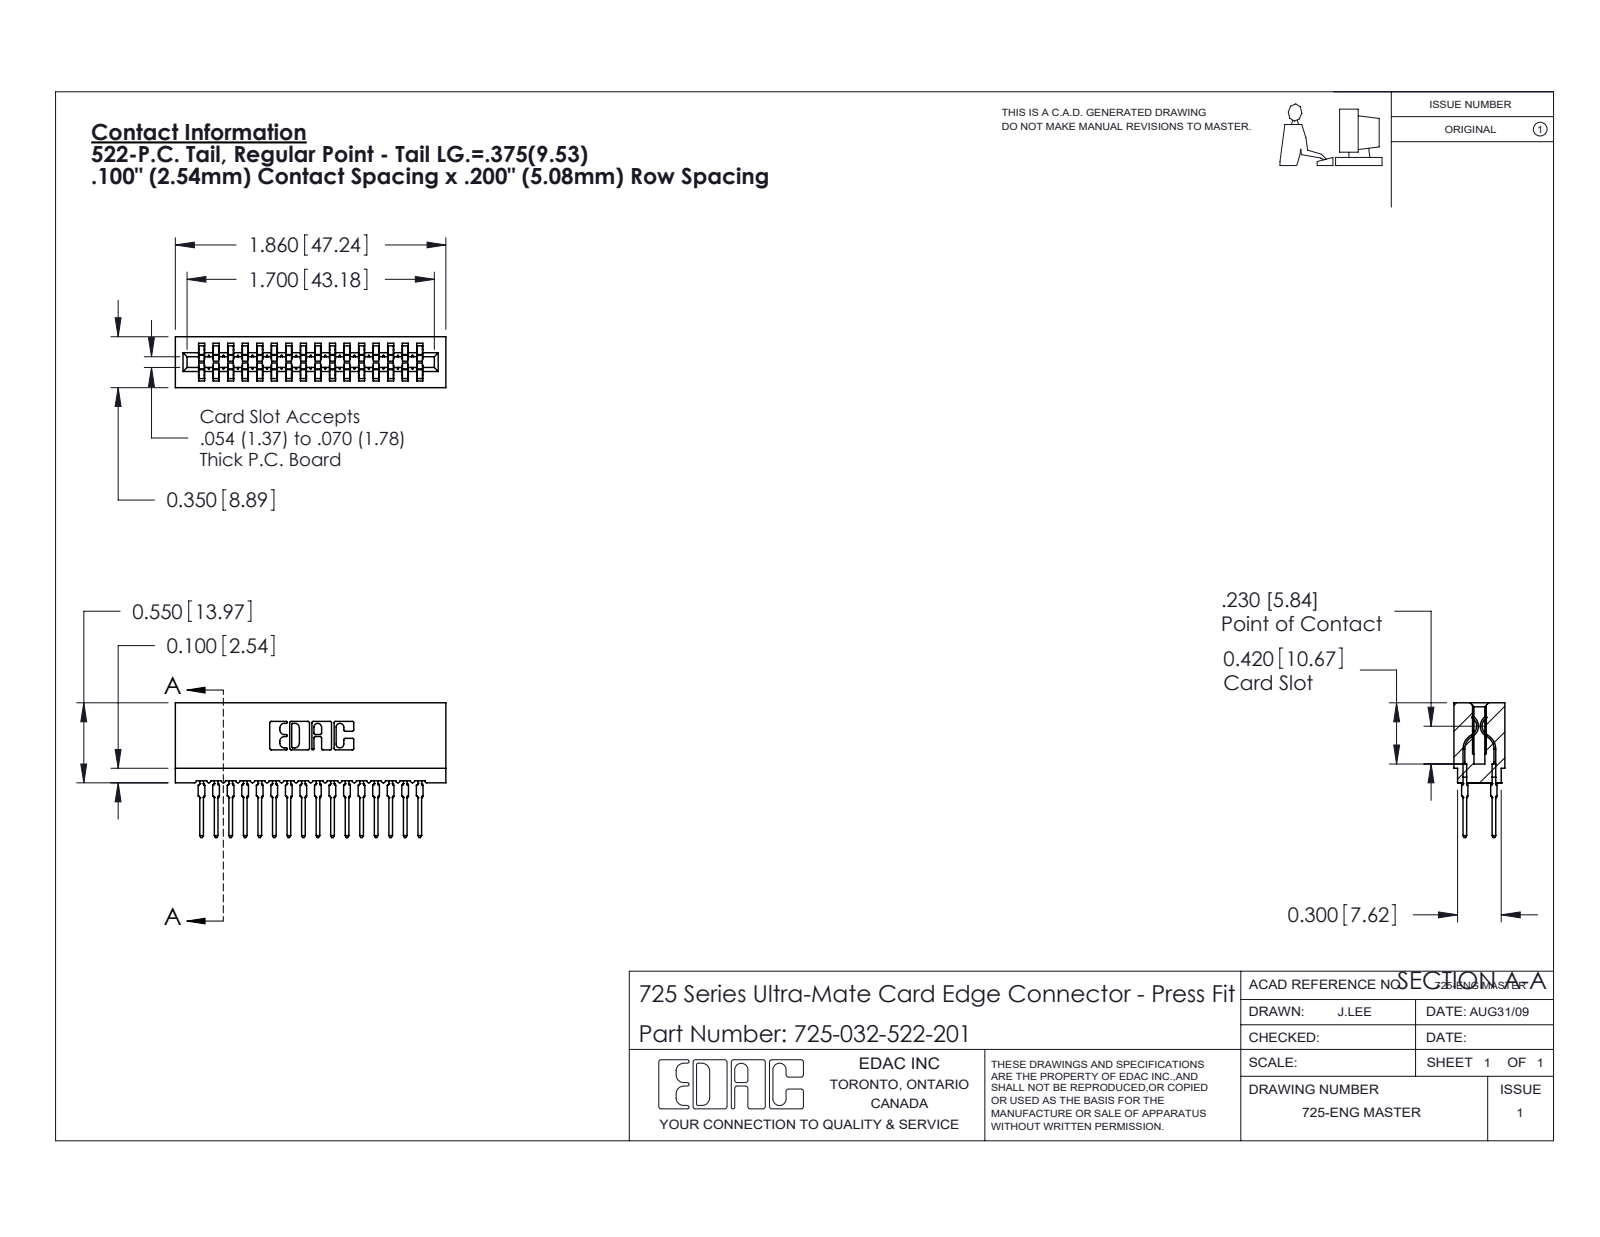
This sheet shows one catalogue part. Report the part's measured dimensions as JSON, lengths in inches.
{"part_name": "725 Part_Insulator Option - 01; 745-292-001_522; 725-032-522-201", "step_written_by": "SolidWorks 2020 (CONFIG_CONTROL_DESIGN)", "units": "inches", "bodies": {"solids": 33, "faces": 2959, "planar": 1527, "cylindrical": 600, "other": 832}, "overall_size": [1.86, 0.926, 0.35], "volume_in3": 0.239, "surface_area_in2": 12.13, "partial_cylinders_radius": [[0.021, 64], [0.015, 32], [0.01, 22], [0.005, 8], [0.011, 8], [0.007, 6], [0.031, 6], [0.026, 3]], "face_to_face_distances": [0.2, 0.1, 0.3, 0.4, 0.5, 0.6, 0.063, 0.287, 0.35, 0.7]}
